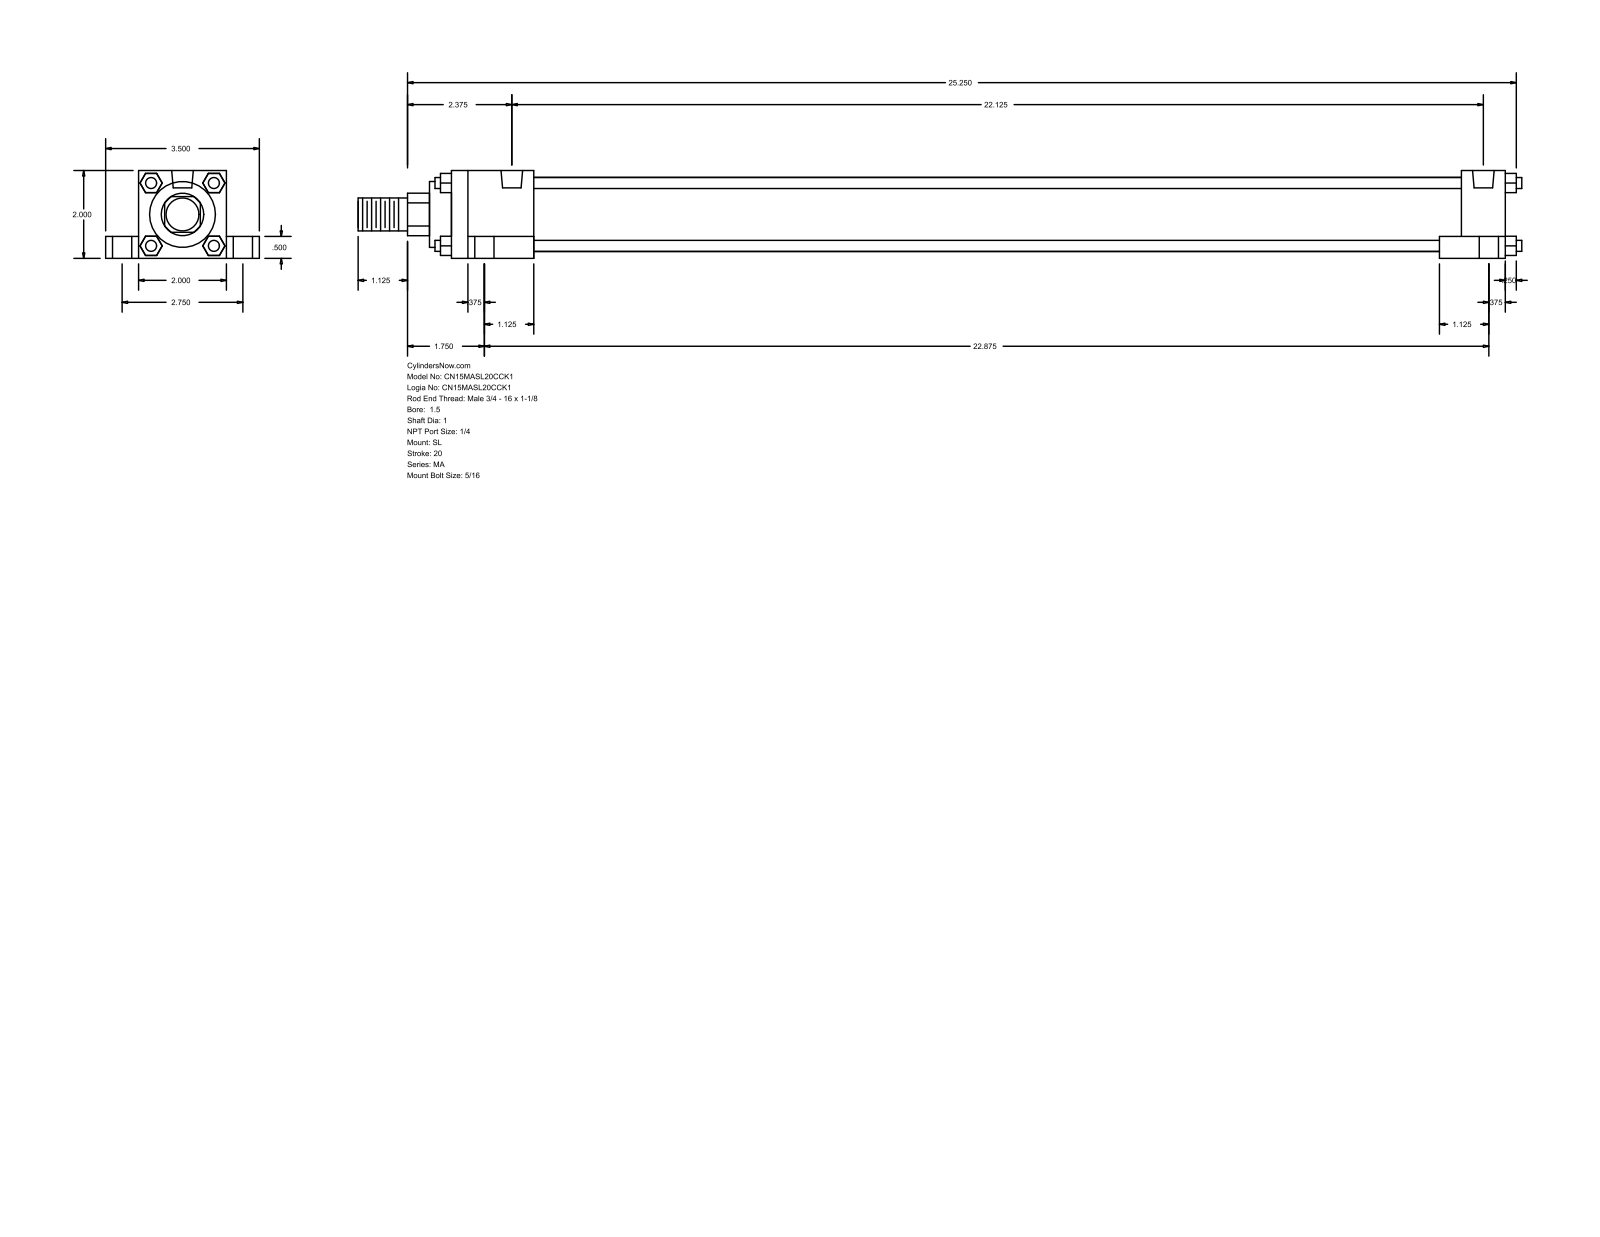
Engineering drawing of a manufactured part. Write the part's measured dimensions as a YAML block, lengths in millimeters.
part_name: "MA_SL__0150_1"
step_written_by: "GSSL Pune (CONFIG_CONTROL_DESIGN)"
units: millimeters
bodies: {solids: 0, faces: 148, planar: 112, cylindrical: 36, other: 0}
overall_size: [673.1, 88.9, 50.8]
round_holes:
  - {diameter: 7.94, count: 4}
  - {diameter: 11.11, count: 4}
  - {diameter: 17.46, count: 4}
  - {diameter: 12.49, count: 2}
round_bosses_or_shafts:
  - {diameter: 6.35, count: 4}
  - {diameter: 42.93, count: 1}
  - {diameter: 38.1, count: 1}
  - {diameter: 25.4, count: 1}
  - {diameter: 19.05, count: 1}
partial_cylinders:
  - {radius: 12.29, count: 1}
face_to_face_distances: [50.8, 12.7, 19.05, 69.85, 38.1, 9.52, 609.6, 25.4, 6.35, 584.2]
hole_center_spacings: [35.06, 38.36, 69.84, 561.97, 566.23, 578.9, 581.03, 585.21]
